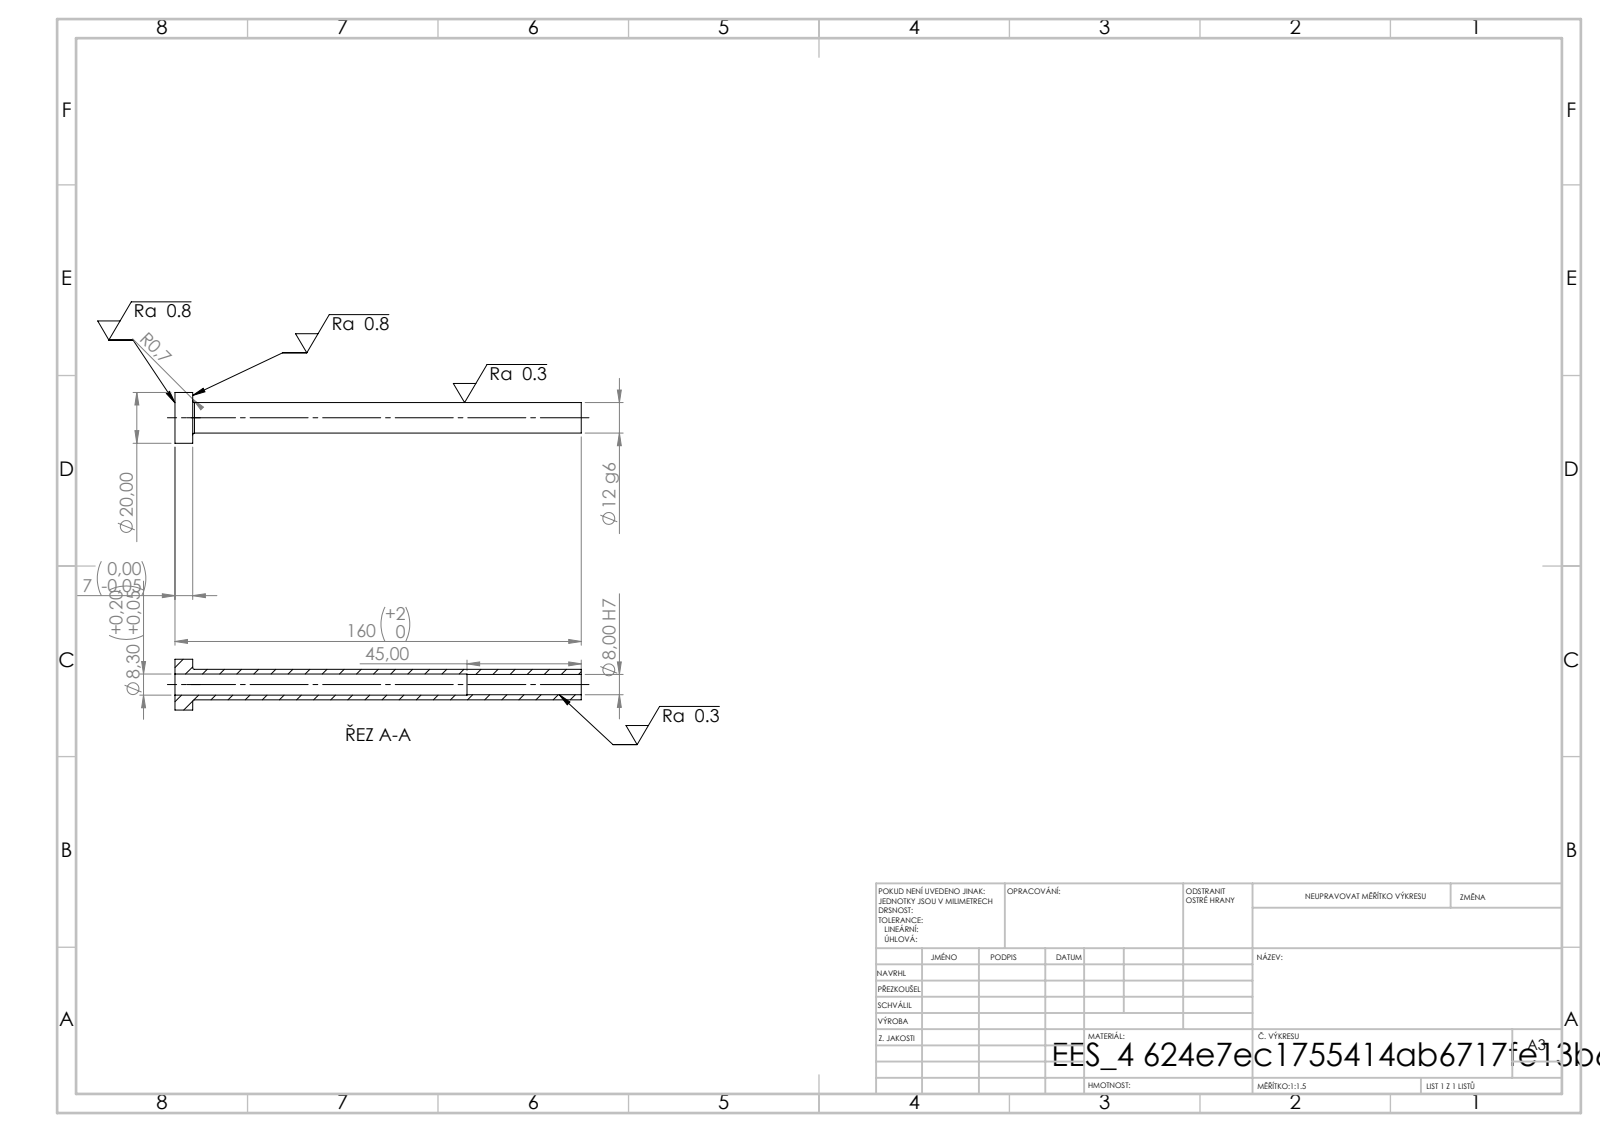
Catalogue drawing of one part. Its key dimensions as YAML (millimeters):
step_written_by: "SolidWorks 2019 (CONFIG_CONTROL_DESIGN)"
units: millimeters
bodies: {solids: 1, faces: 14, planar: 4, cylindrical: 8, other: 2}
overall_size: [160, 20, 20]
volume: 11023
surface_area: 10854
round_holes:
  - {diameter: 8, count: 1}
  - {diameter: 8.3, count: 1}
round_bosses_or_shafts:
  - {diameter: 20, count: 1}
  - {diameter: 12, count: 1}
face_to_face_distances: [7, 160, 153, 115, 108, 45]
